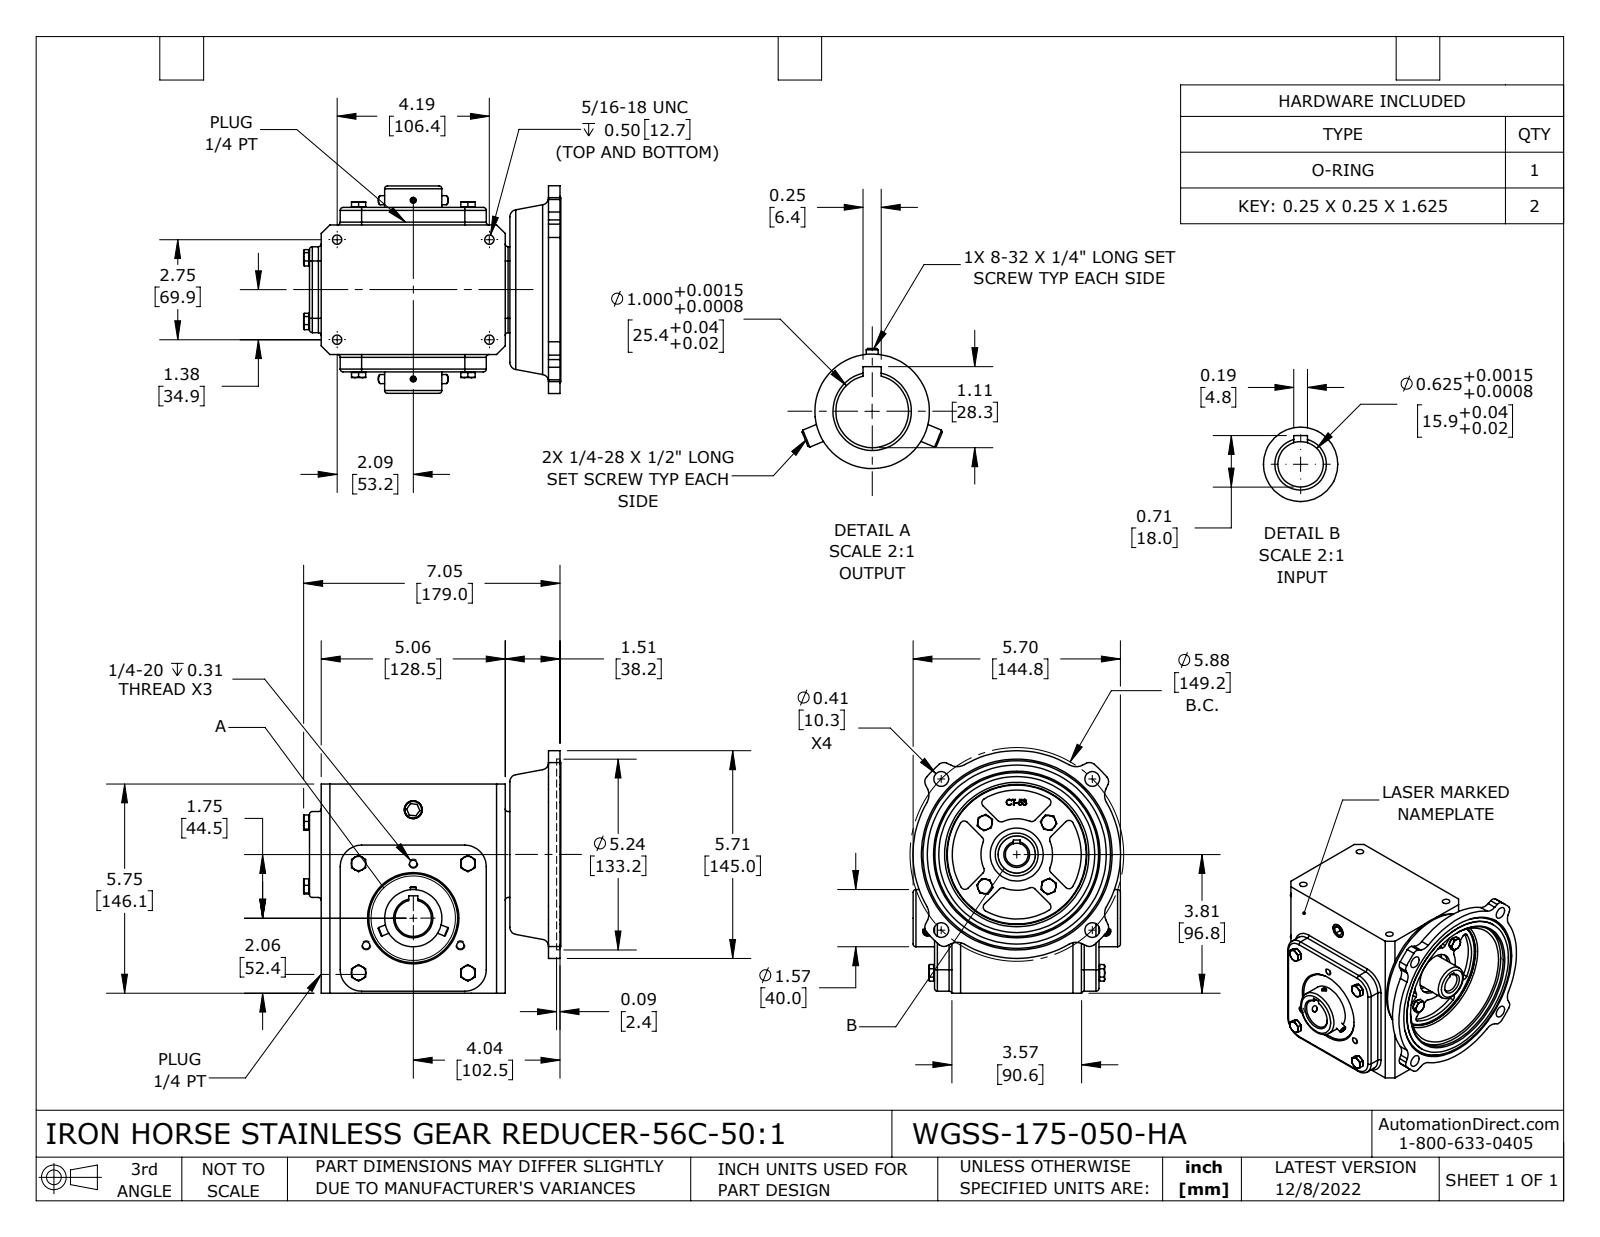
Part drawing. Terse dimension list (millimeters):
name: WGSS-175-050-HA
written by: SolidWorks 2021 (CONFIG_CONTROL_DESIGN)
unit: mm
bodies: 7 solids, 891 faces (390 planar, 231 cylindrical, 270 other)
size: 179.6 × 170 × 145
volume: 2 081 000 mm³; area: 181 300 mm²
holes: 4× ⌀5.4, 4× ⌀6.5, 4× ⌀10.3, 3× ⌀5.1, 2× ⌀3.5, 1× ⌀15.9, 1× ⌀22, 1× ⌀25.4, 1× ⌀28, 1× ⌀37, 1× ⌀40, 1× ⌀97
bosses: 8× ⌀10, 4× ⌀6.4, 2× ⌀4.2, 1× ⌀125, 1× ⌀62, 1× ⌀40, 1× ⌀30
rounds: 28× R2, 16× R3, 12× R10, 8× R5, 4× R15, 1× R25, 1× R45, 1× R72.5
face distances: 12.2, 102.6, 146.1, 128.5, 4, 90.4, 114.8, 8, 166.8, 38.3
hole spacings: 59.9, 74.6, 105.5, 38, 65.8, 124.8, 69.9, 106.4
